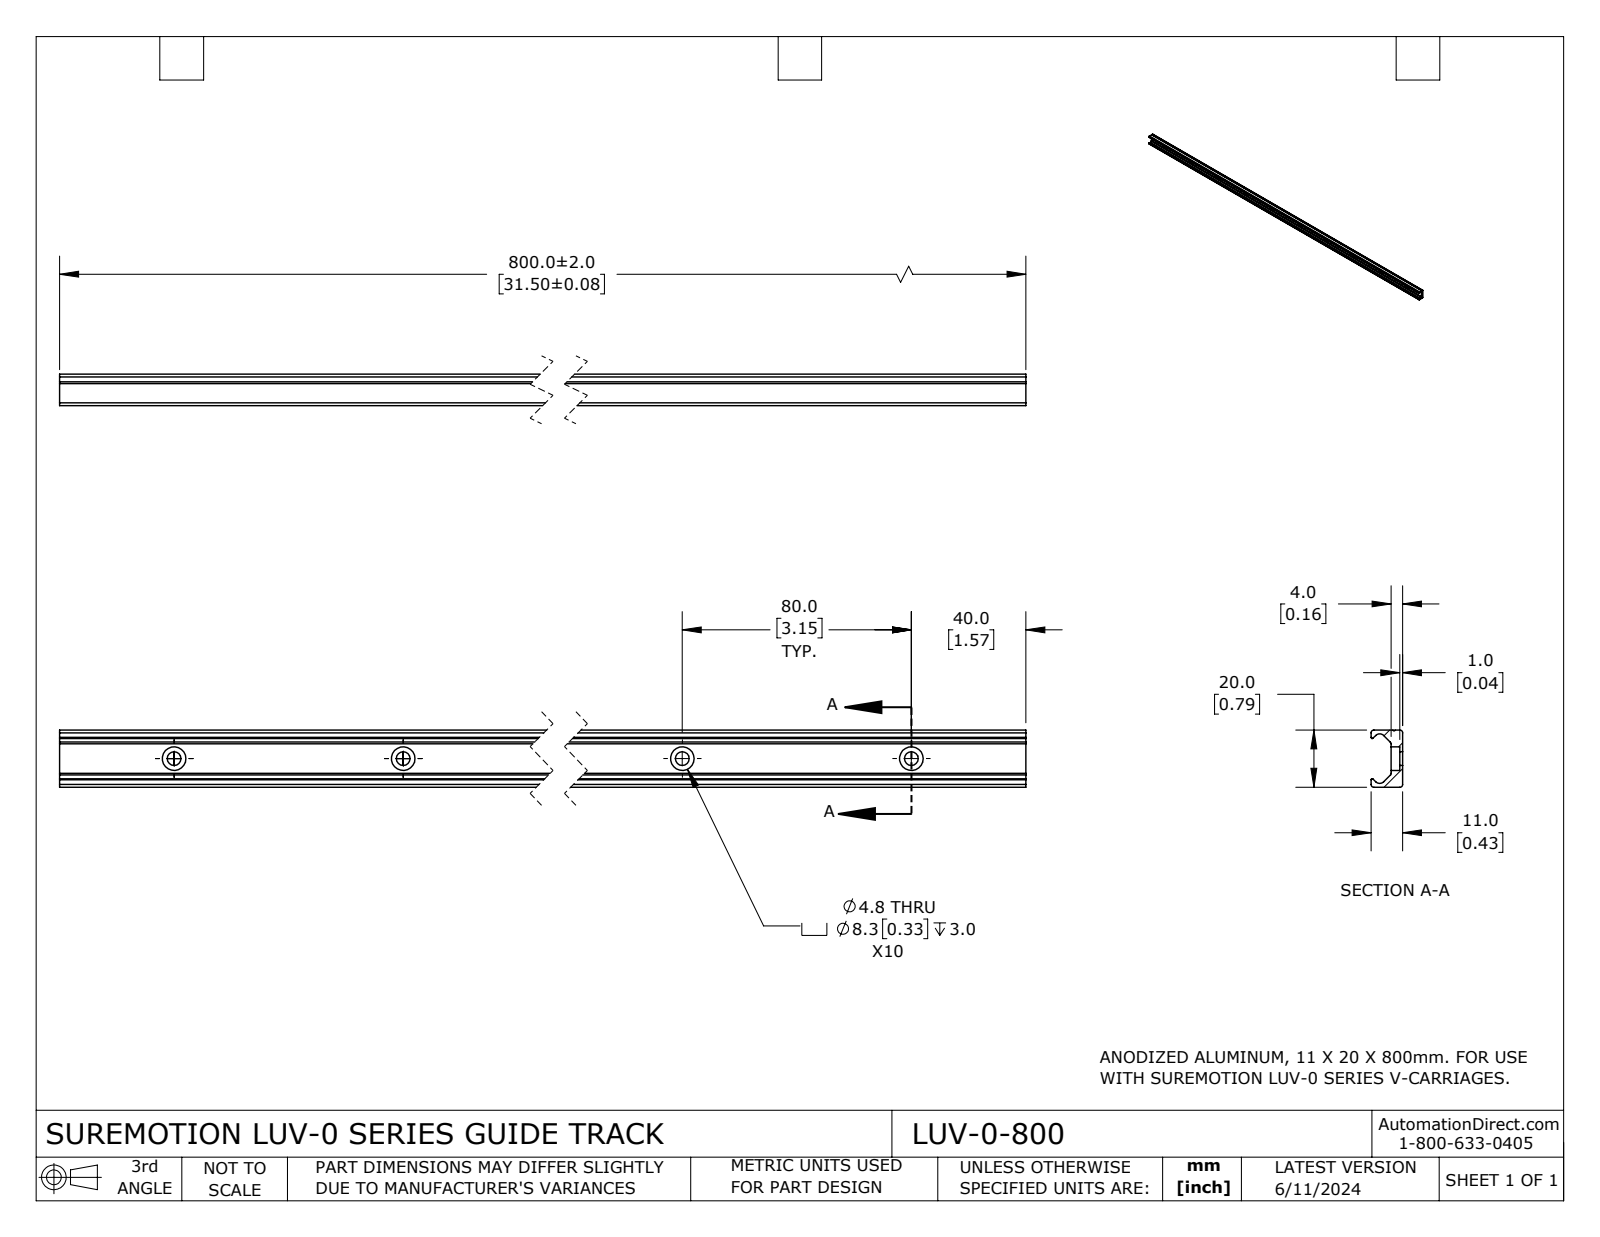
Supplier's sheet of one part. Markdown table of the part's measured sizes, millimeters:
| quantity | value |
| --- | --- |
| part name | LUV-0-800 |
| STEP written by | SolidWorks 2023 (CONFIG_CONTROL_DESIGN) |
| units | millimeters |
| bodies | 1 solid, 76 faces (23 planar, 53 cylindrical, 0 other) |
| overall size | 800 × 19.99 × 11 |
| volume | 88 296 mm³ |
| surface area | 60 620 mm² |
| round holes (diameter × count) | 4.8 × 10, 8.25 × 5, 8.26 × 5 |
| partial cylindrical surfaces (radius × count) | 0.99 × 4, 0.38 × 2, 0.4 × 2, 0.79 × 2, 1.98 × 2, 0.33 × 1 |
| main face-to-face distances | 4.01, 20, 11, 6.99, 13.4, 1.01, 3, 9.99, 800 |
| hole center spacings | 80, 160, 240, 320, 400, 480, 560, 640 |
